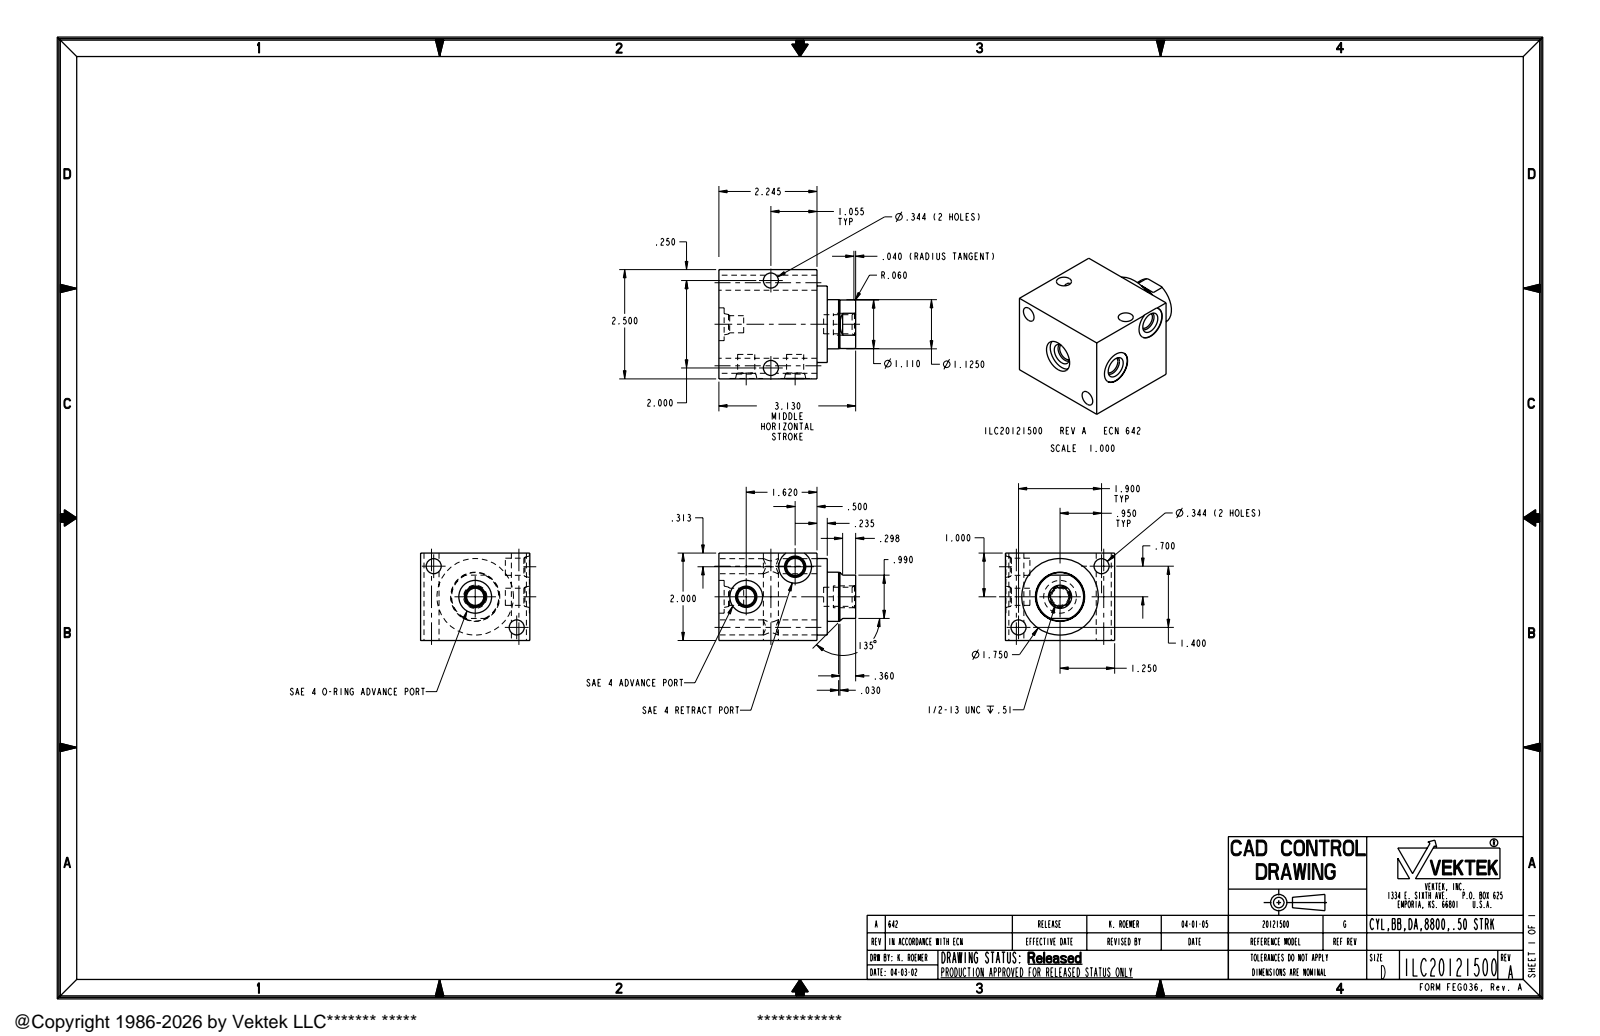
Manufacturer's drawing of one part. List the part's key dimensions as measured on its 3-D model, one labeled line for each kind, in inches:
Part name (STEP PRODUCT): ILC20121500
STEP written by: PRO/ENGINEER BY PARAMETRIC TECHNOLOGY CORPORATION, 2004290 (AUTOMOTIVE_DESIGN_CC2)
Units: inches
Bodies: 1 solid, 71 faces (20 planar, 33 cylindrical, 18 other)
Overall size (bounding box): 3.13 × 2.5 × 2
Volume: 11.3 in³ · Surface area: 45.14 in²
Round holes (diameter × count): ⌀0.344 ×4, ⌀0.392 ×3, ⌀0.75 ×3, ⌀0.437 ×1
Round bosses / shafts (diameter × count): ⌀1.75 ×1, ⌀1.125 ×1, ⌀1.11 ×1, ⌀0.5 ×1
Main face-to-face distances: 2, 2.5, 2.245, 0.235, 2.48, 0.65, 0.885, 3.13, 2.49, 0.505
Hole centre spacings: 1.18, 1.314, 2, 2.36
